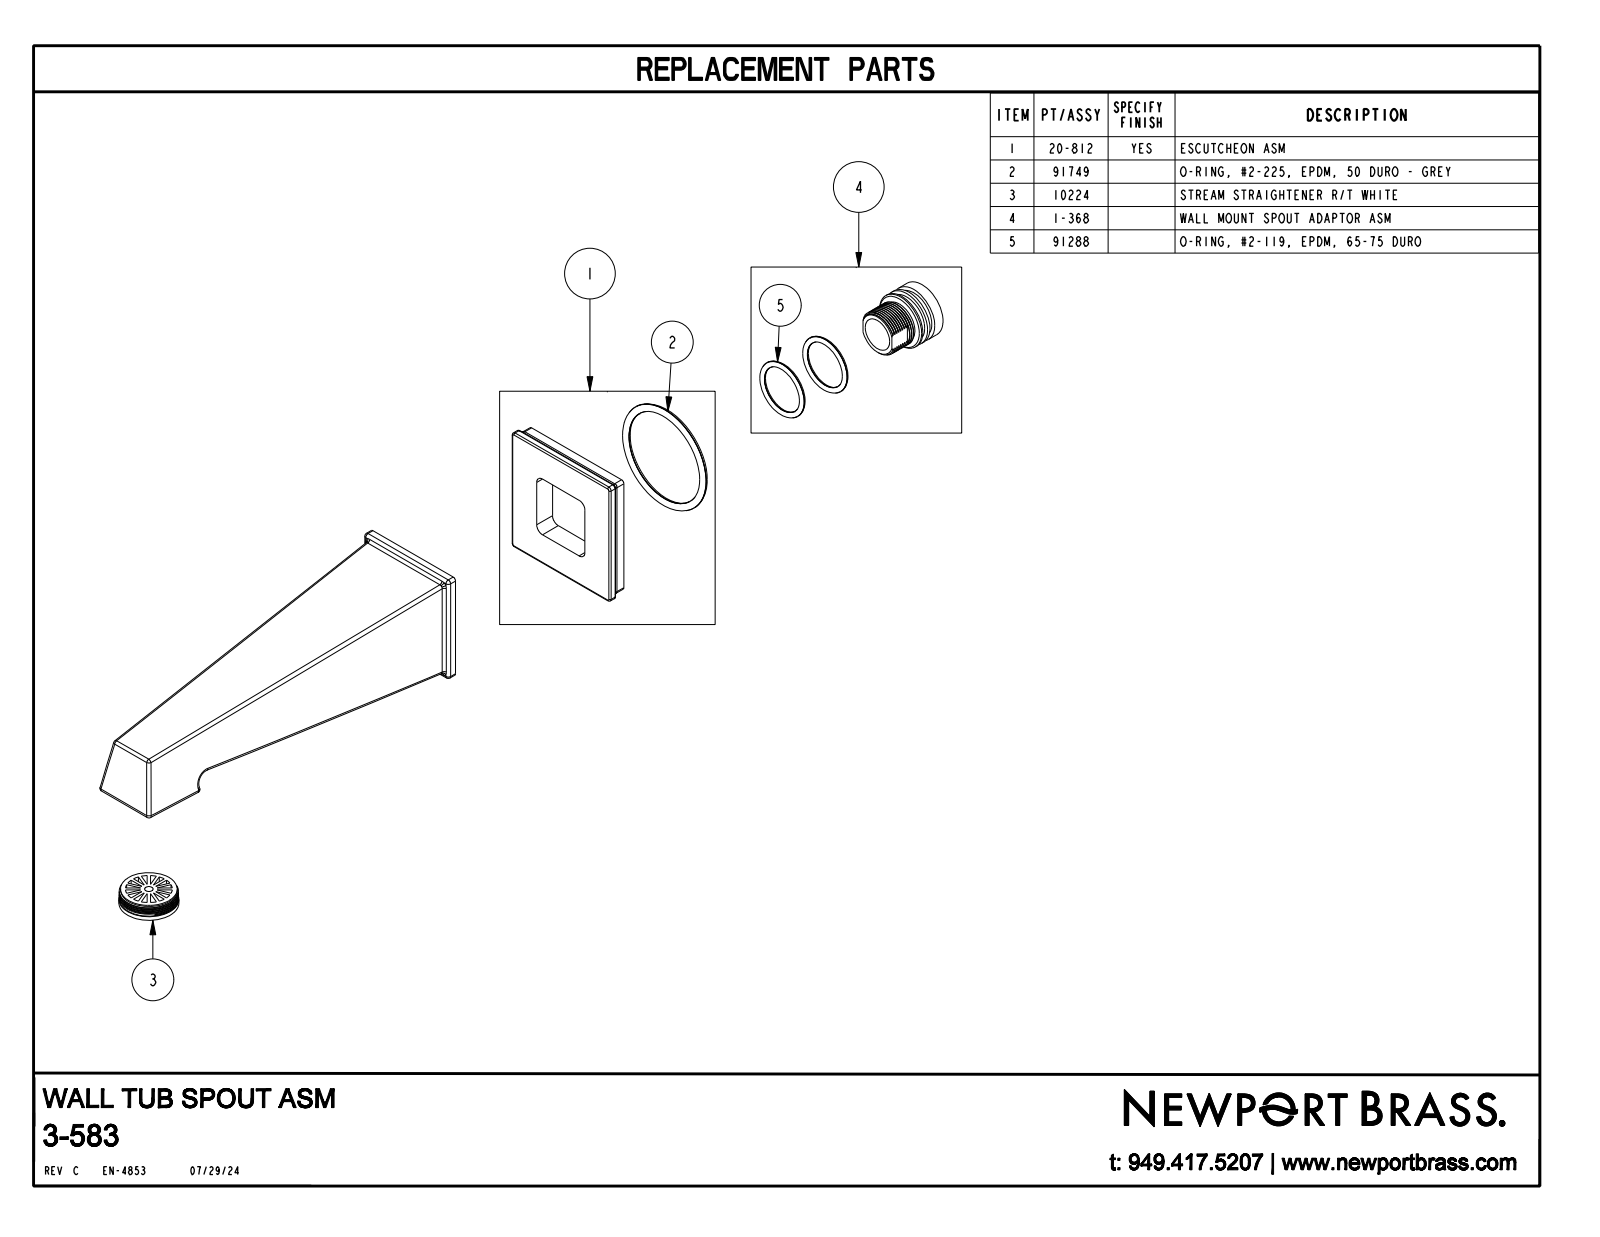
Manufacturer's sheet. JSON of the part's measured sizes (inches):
{"part_name": "3-583", "step_written_by": "CREO PARAMETRIC BY PTC INC, 2018400 (AUTOMOTIVE_DESIGN)", "units": "inches", "bodies": {"solids": 1, "faces": 140, "planar": 28, "cylindrical": 38, "other": 74}, "overall_size": [7.921, 2.55, 2.55], "volume_in3": 19.53, "surface_area_in2": 62.51, "partial_cylinders_radius": [[0.06, 21], [0.03, 8], [0.09, 4], [0.317, 4], [0.2, 1]], "face_to_face_distances": [0.41, 0.42, 0.125, 2.325, 0.05, 0.175, 2.375, 2.5, 2.45, 2.2]}
